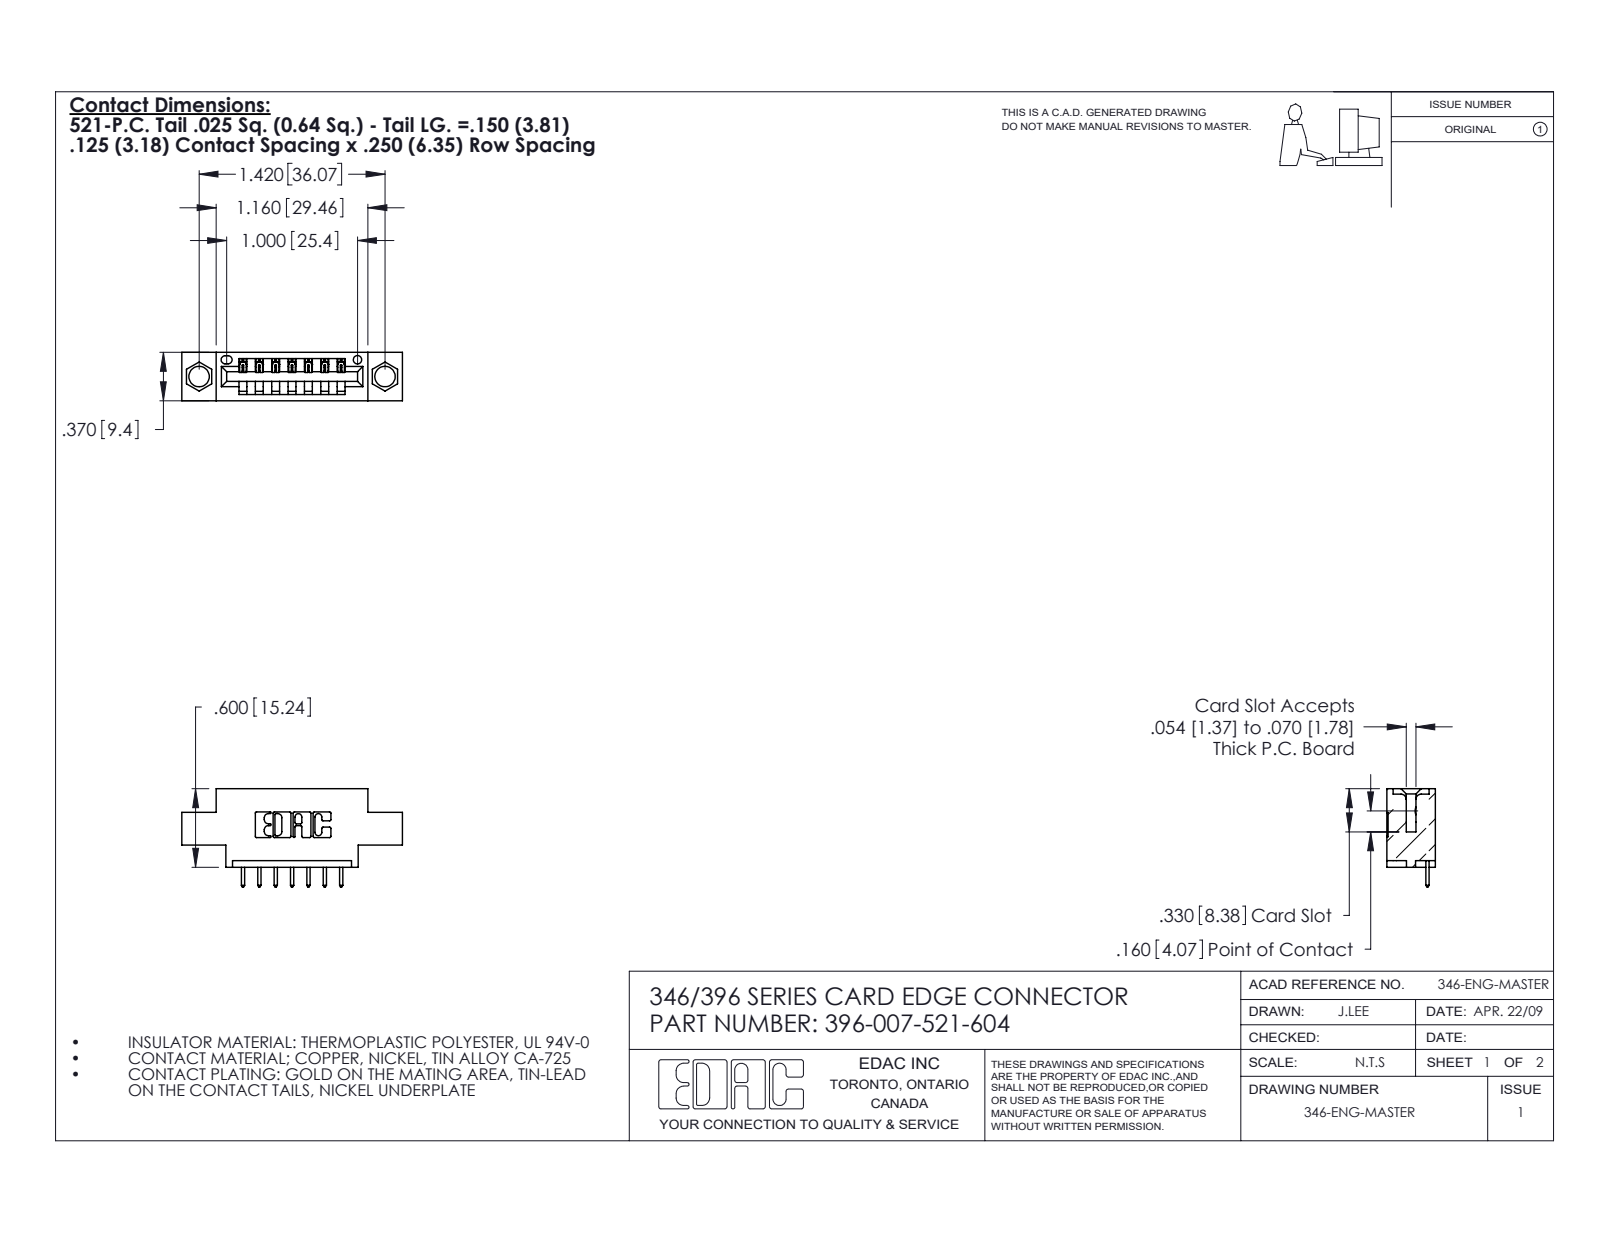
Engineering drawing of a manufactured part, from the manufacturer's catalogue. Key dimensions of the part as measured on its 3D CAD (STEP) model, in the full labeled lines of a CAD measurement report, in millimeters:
Part name (STEP PRODUCT): 345-292-001_345-293-121; 346 Part_0.170 Offset - 0.156 Dia-TH; 396-007-521-604
STEP written by: SolidWorks 2020 (CONFIG_CONTROL_DESIGN)
Units: millimetres
Bodies: 8 solids, 546 faces (374 planar, 172 cylindrical, 0 other)
Overall size (bounding box): 42.8 × 19.1 × 9.4
Volume: 3 570 mm³ · Surface area: 4 009 mm²
Round holes (diameter × count): ⌀4 ×2, ⌀1.6 ×1
Partial cylindrical surfaces — rounded edges, fillets, slot ends (radius × count): R0.3 ×22, R0.2 ×14, R0.3 ×14, R0.2 ×6, R0.8 ×6, R0.7 ×3, R0.8 ×2, R1 ×2
Main face-to-face distances: 6.4, 9.4, 1.2, 8.2, 5.6, 3.8, 2.5, 4.4, 3.2, 4.7
Hole centre spacings: 6.2, 30.9, 36.1
